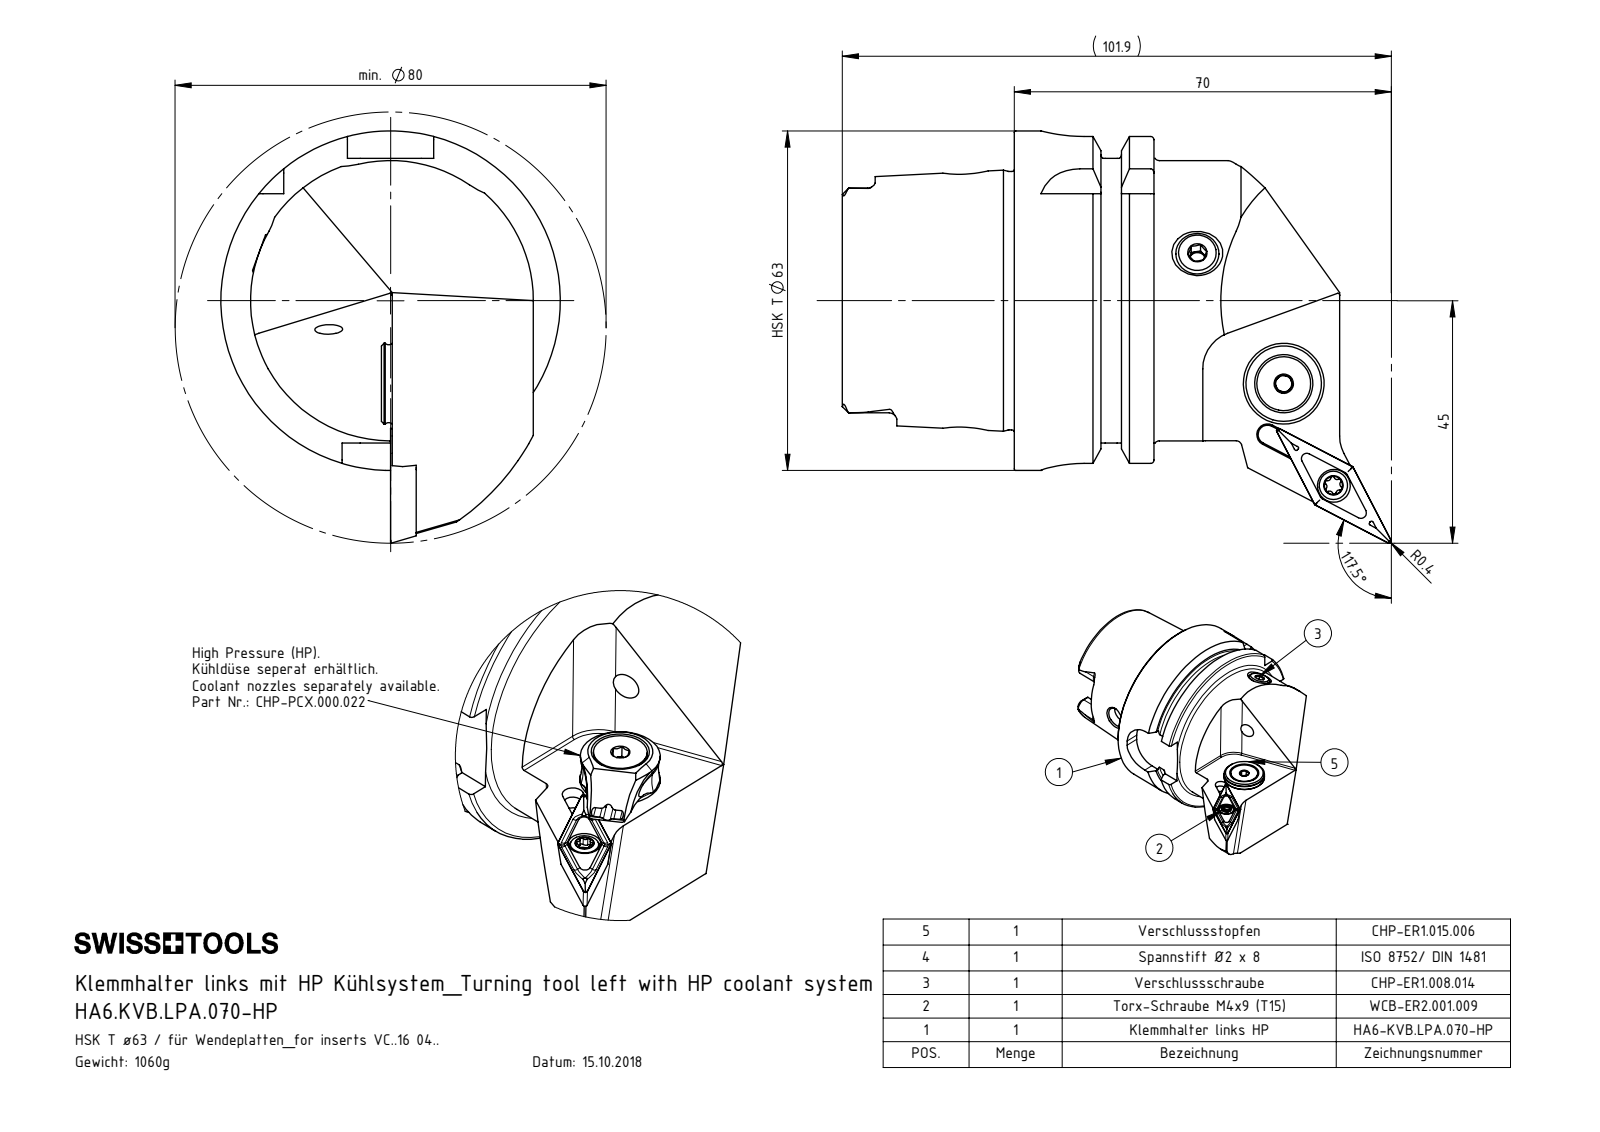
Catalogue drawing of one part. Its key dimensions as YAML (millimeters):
part_name: "WCB-ER2.001.009_A; HA6-KVB.LPA.070-HP_A; ISO 8752 2x8; CHP-ER1.015.006 (+6 more)"
step_written_by: "SolidWorks 2017 (AUTOMOTIVE_DESIGN)"
units: millimeters
bodies: {solids: 8, faces: 316, planar: 121, cylindrical: 77, other: 118}
overall_size: [101.9, 76.5, 63]
volume: 134823
surface_area: 32235
round_holes:
  - {diameter: 4.2, count: 2}
  - {diameter: 5, count: 2}
  - {diameter: 1.2, count: 1}
  - {diameter: 2, count: 1}
  - {diameter: 2.5, count: 1}
  - {diameter: 3, count: 1}
  - {diameter: 3.3, count: 1}
  - {diameter: 4.4, count: 1}
  - {diameter: 5.2, count: 1}
  - {diameter: 6.1, count: 1}
  - {diameter: 7, count: 1}
  - {diameter: 7.5, count: 1}
round_bosses_or_shafts:
  - {diameter: 63, count: 1}
  - {diameter: 54.95, count: 1}
  - {diameter: 52, count: 1}
  - {diameter: 47.94, count: 1}
  - {diameter: 15, count: 1}
  - {diameter: 13.4, count: 1}
  - {diameter: 10, count: 1}
  - {diameter: 8, count: 1}
partial_cylinders:
  - {radius: 0.34, count: 6}
  - {radius: 0.59, count: 6}
  - {radius: 1.4, count: 6}
  - {radius: 8, count: 4}
  - {radius: 0.5, count: 2}
  - {radius: 2.82, count: 2}
  - {radius: 2.88, count: 2}
  - {radius: 7, count: 2}
face_to_face_distances: [25.95, 16, 9.95, 26.2, 31.9, 41.85, 57.85, 52.8, 21.8, 11.85]
hole_center_spacings: [4.5, 17.3, 17.41, 21, 21.11, 45.7, 47.05, 62.49]
